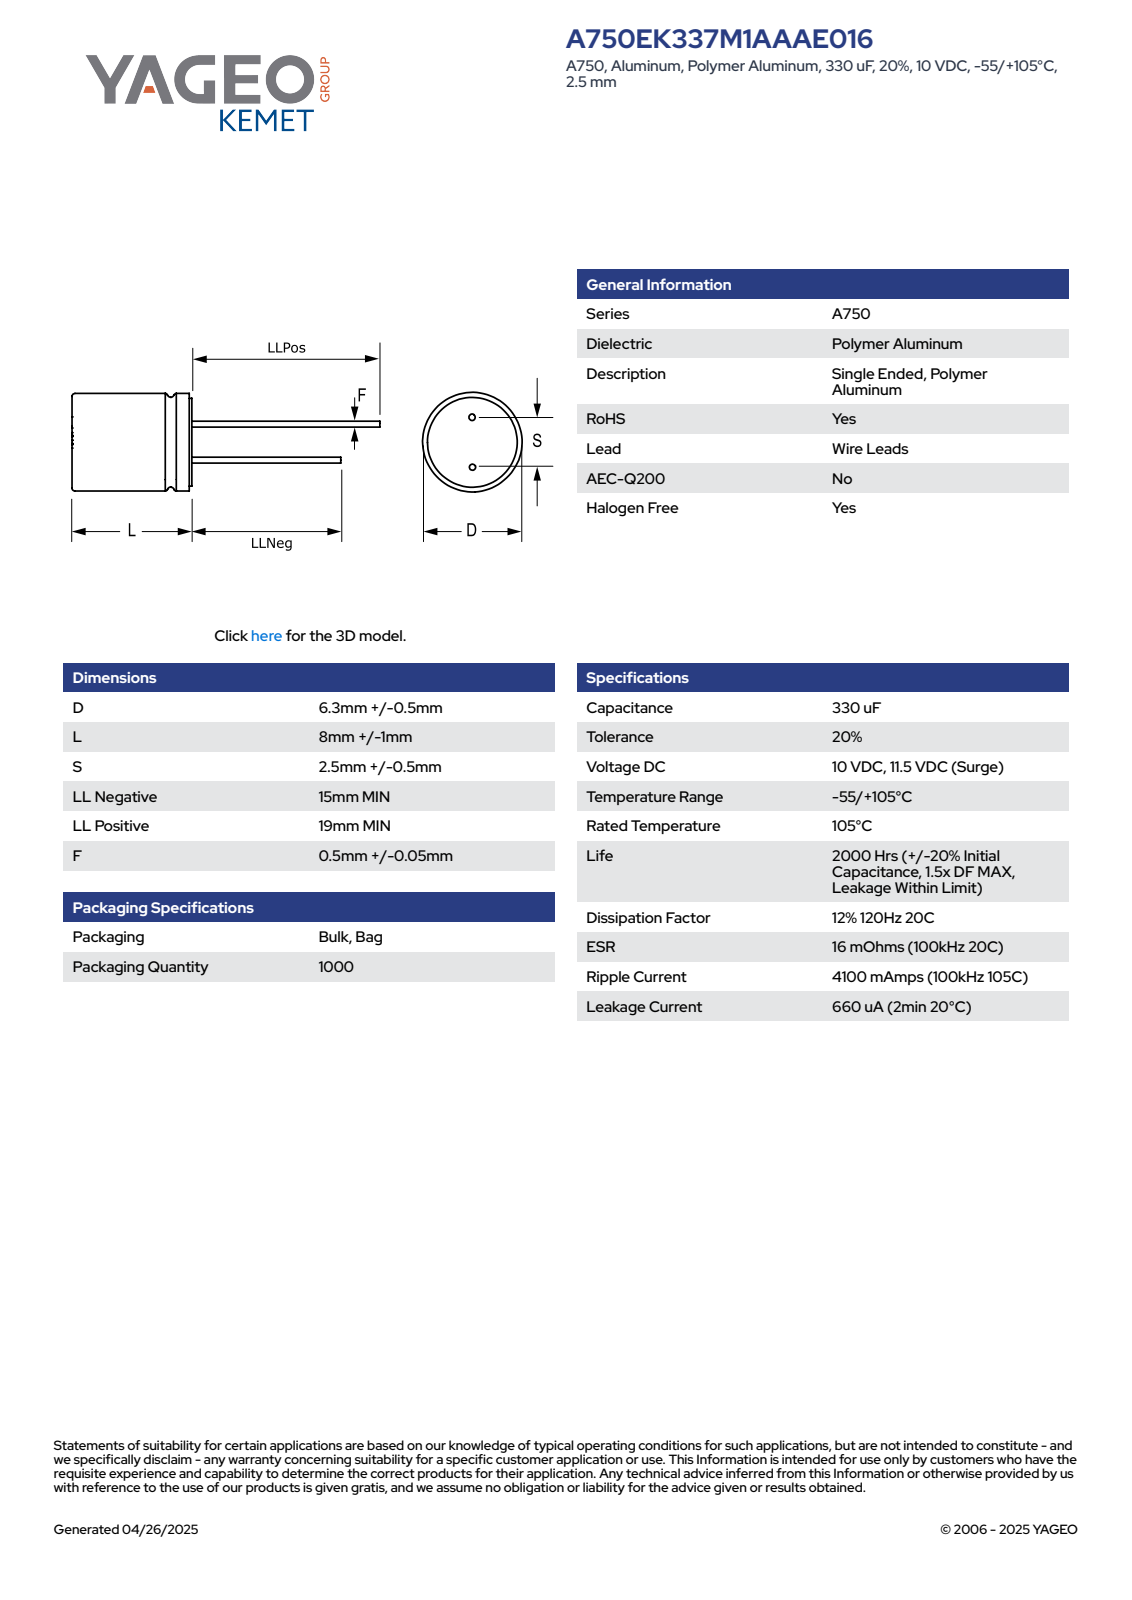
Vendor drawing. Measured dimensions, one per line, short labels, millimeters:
name: CAR_KP_6.3X8_D6.8L9S2.5F0.55
written by: SolidWorks 2014 (AUTOMOTIVE_DESIGN)
unit: mm
bodies: 4 solids, 75 faces (61 planar, 8 cylindrical, 6 other)
size: 28 × 6.8 × 6.8
volume: 332 mm³; area: 331 mm²
bosses: 2× ⌀0.55, 1× ⌀6.8
face distances: 9, 9.01, 24.01, 28.01, 24, 28, 15, 19, 4, 0.75
